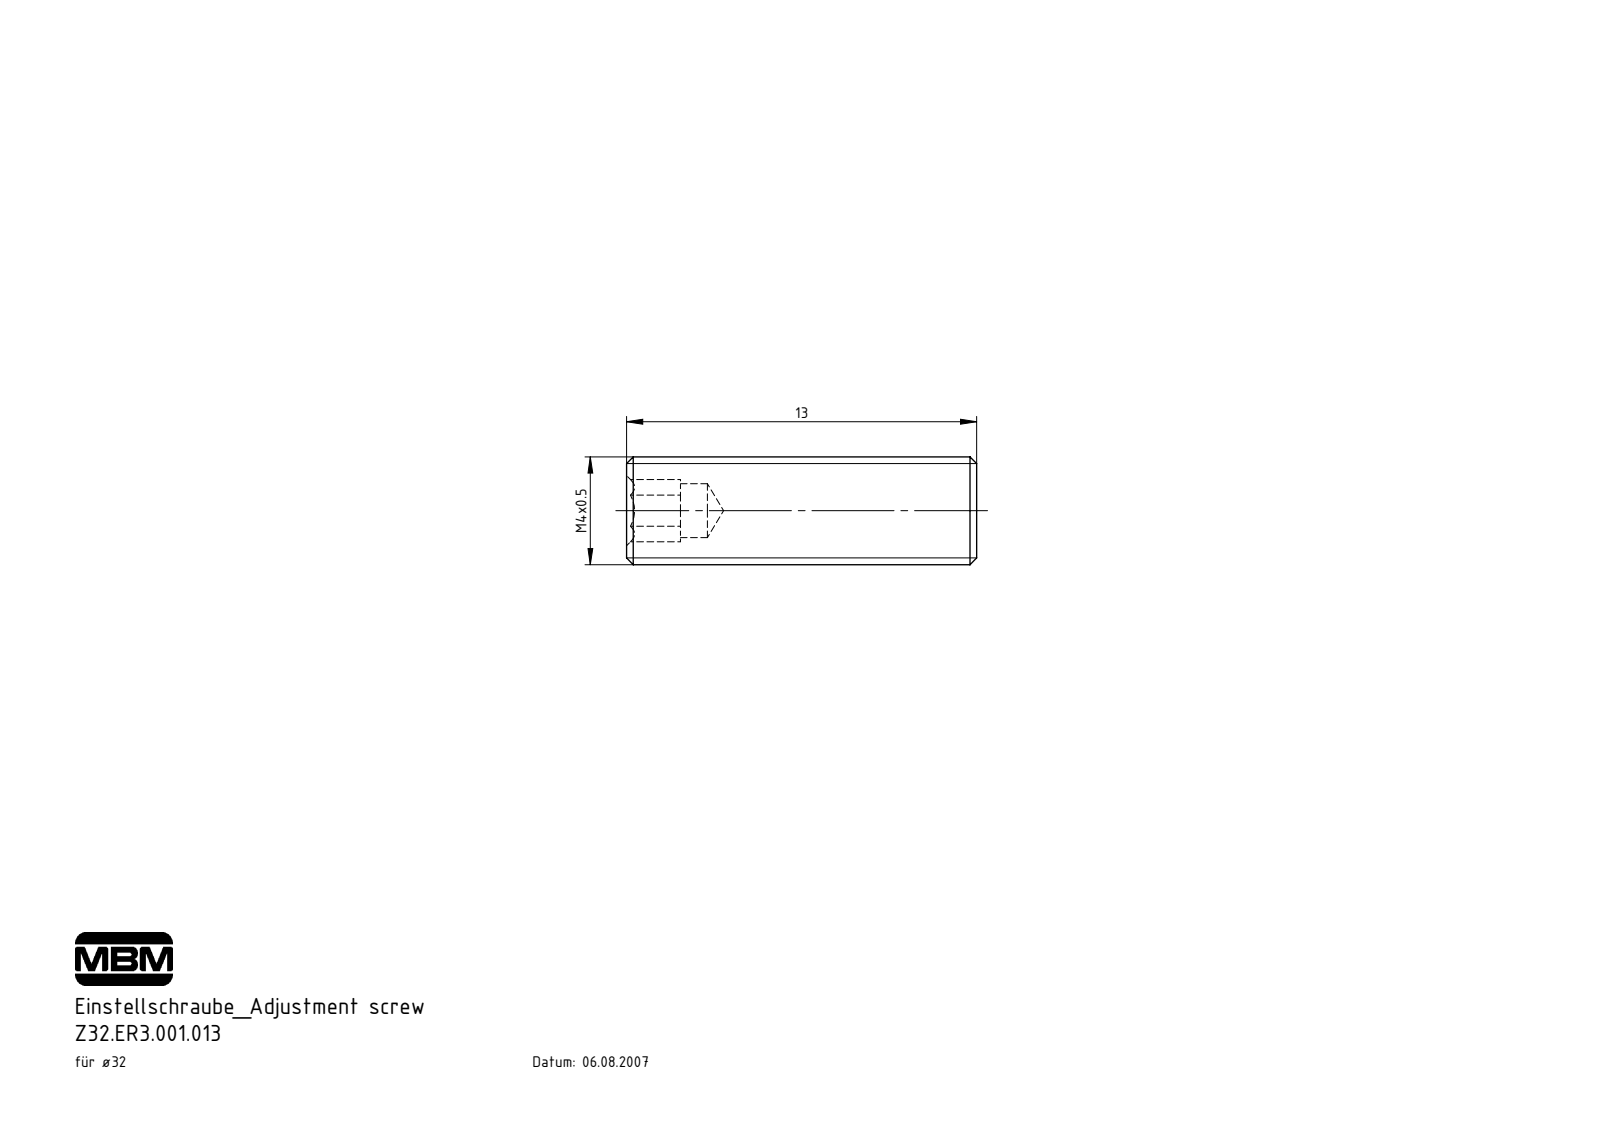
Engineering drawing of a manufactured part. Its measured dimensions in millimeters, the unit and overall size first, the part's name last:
Units: millimetres
Overall size (bounding box): 13 × 4 × 4
Round holes (diameter × count): ⌀2 ×1
Round bosses / shafts (diameter × count): ⌀4 ×1
Main face-to-face distances: 2, 13, 11
Volume: 152 mm³ · Surface area: 204 mm²
Bodies: 1 solid, 26 faces (14 planar, 4 cylindrical, 8 other)
Part name (STEP PRODUCT): Z32.ER3.001.013
STEP written by: SolidWorks 2017 (AUTOMOTIVE_DESIGN)
